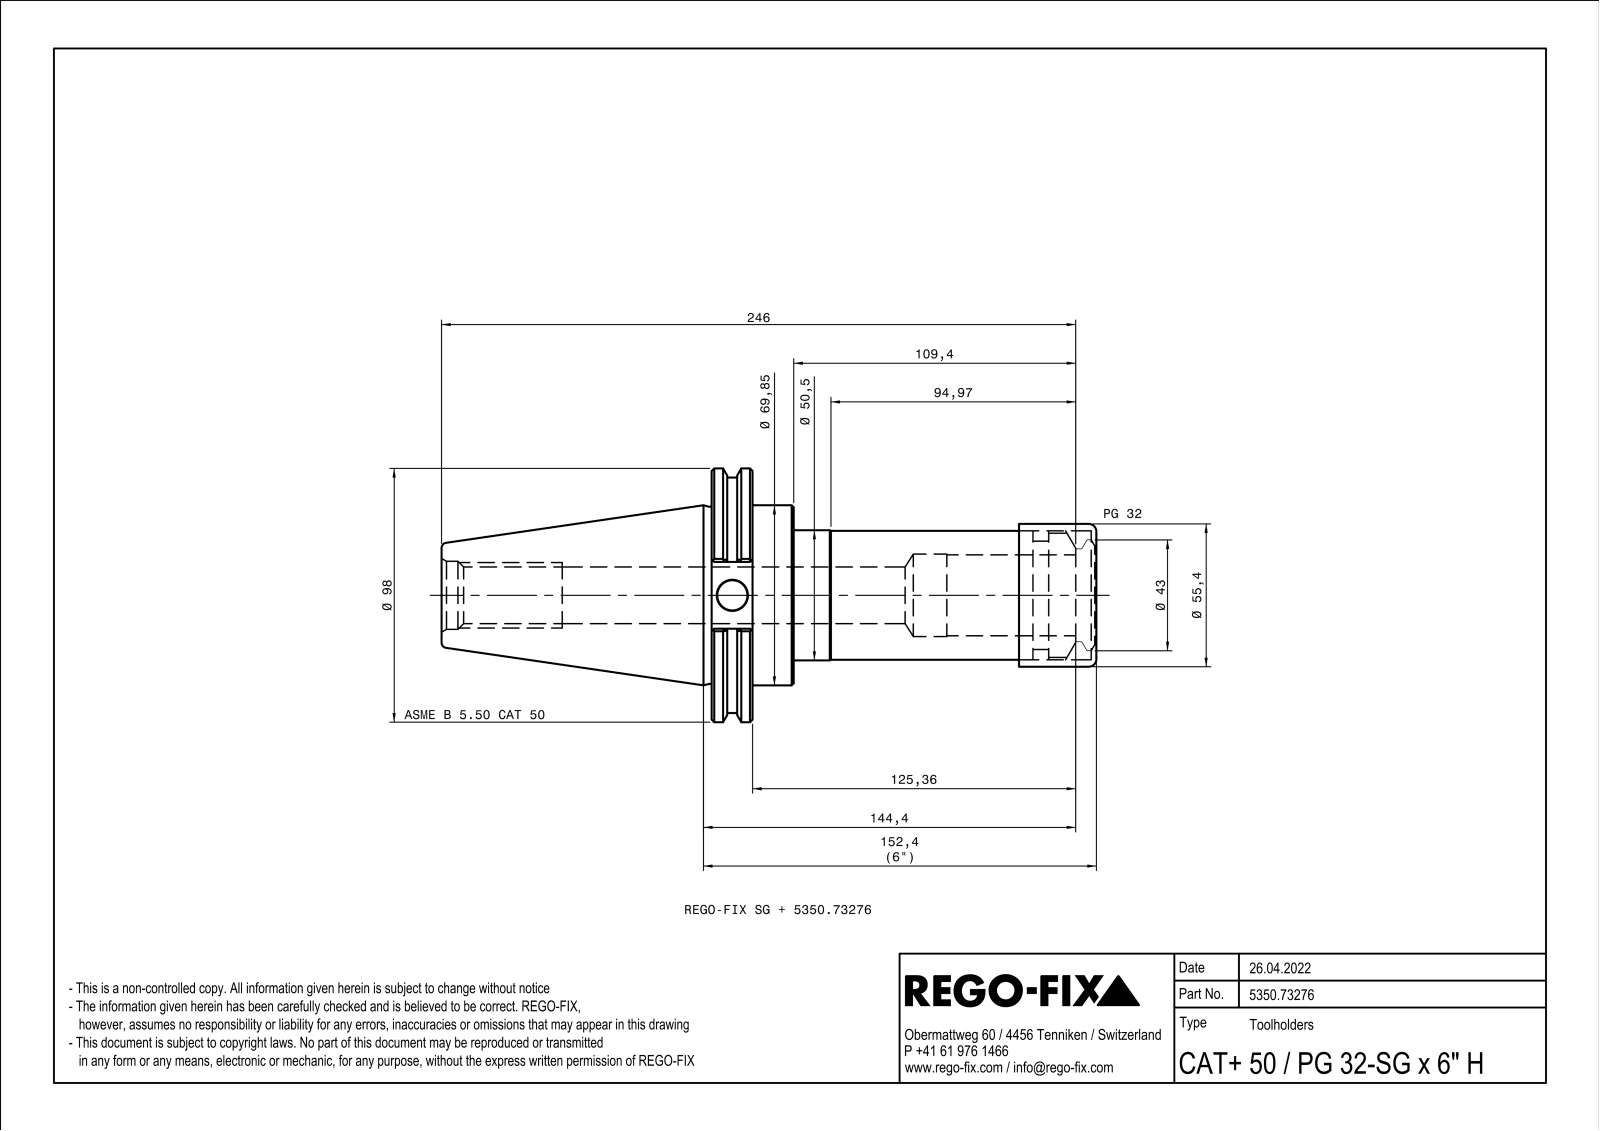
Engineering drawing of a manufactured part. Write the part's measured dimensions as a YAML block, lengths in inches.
part_name: "NOCUT"
step_written_by: "SIEMENS PLM Software Solid Edge ST10 (AUTOMOTIVE_DESIGN)"
units: inches
bodies: {solids: 1, faces: 124, planar: 55, cylindrical: 25, other: 44}
overall_size: [10, 3.875, 3.718]
volume: 32.45
surface_area: 132.3
round_holes:
  - {diameter: 0.472, count: 1}
  - {diameter: 0.865, count: 1}
  - {diameter: 1.039, count: 1}
  - {diameter: 1.299, count: 1}
  - {diameter: 1.506, count: 1}
  - {diameter: 1.905, count: 1}
  - {diameter: 1.97, count: 1}
  - {diameter: 2.008, count: 1}
round_bosses_or_shafts:
  - {diameter: 3.875, count: 1}
  - {diameter: 3.594, count: 1}
  - {diameter: 2.75, count: 1}
  - {diameter: 2.726, count: 1}
  - {diameter: 2.181, count: 1}
  - {diameter: 2.165, count: 1}
  - {diameter: 1.988, count: 1}
  - {diameter: 1.969, count: 1}
partial_cylinders:
  - {radius: 0.02, count: 4}
face_to_face_distances: [0.691, 0.63, 1.321, 4.62, 5.25, 5.941, 10, 5.38, 4.75, 4.059]
